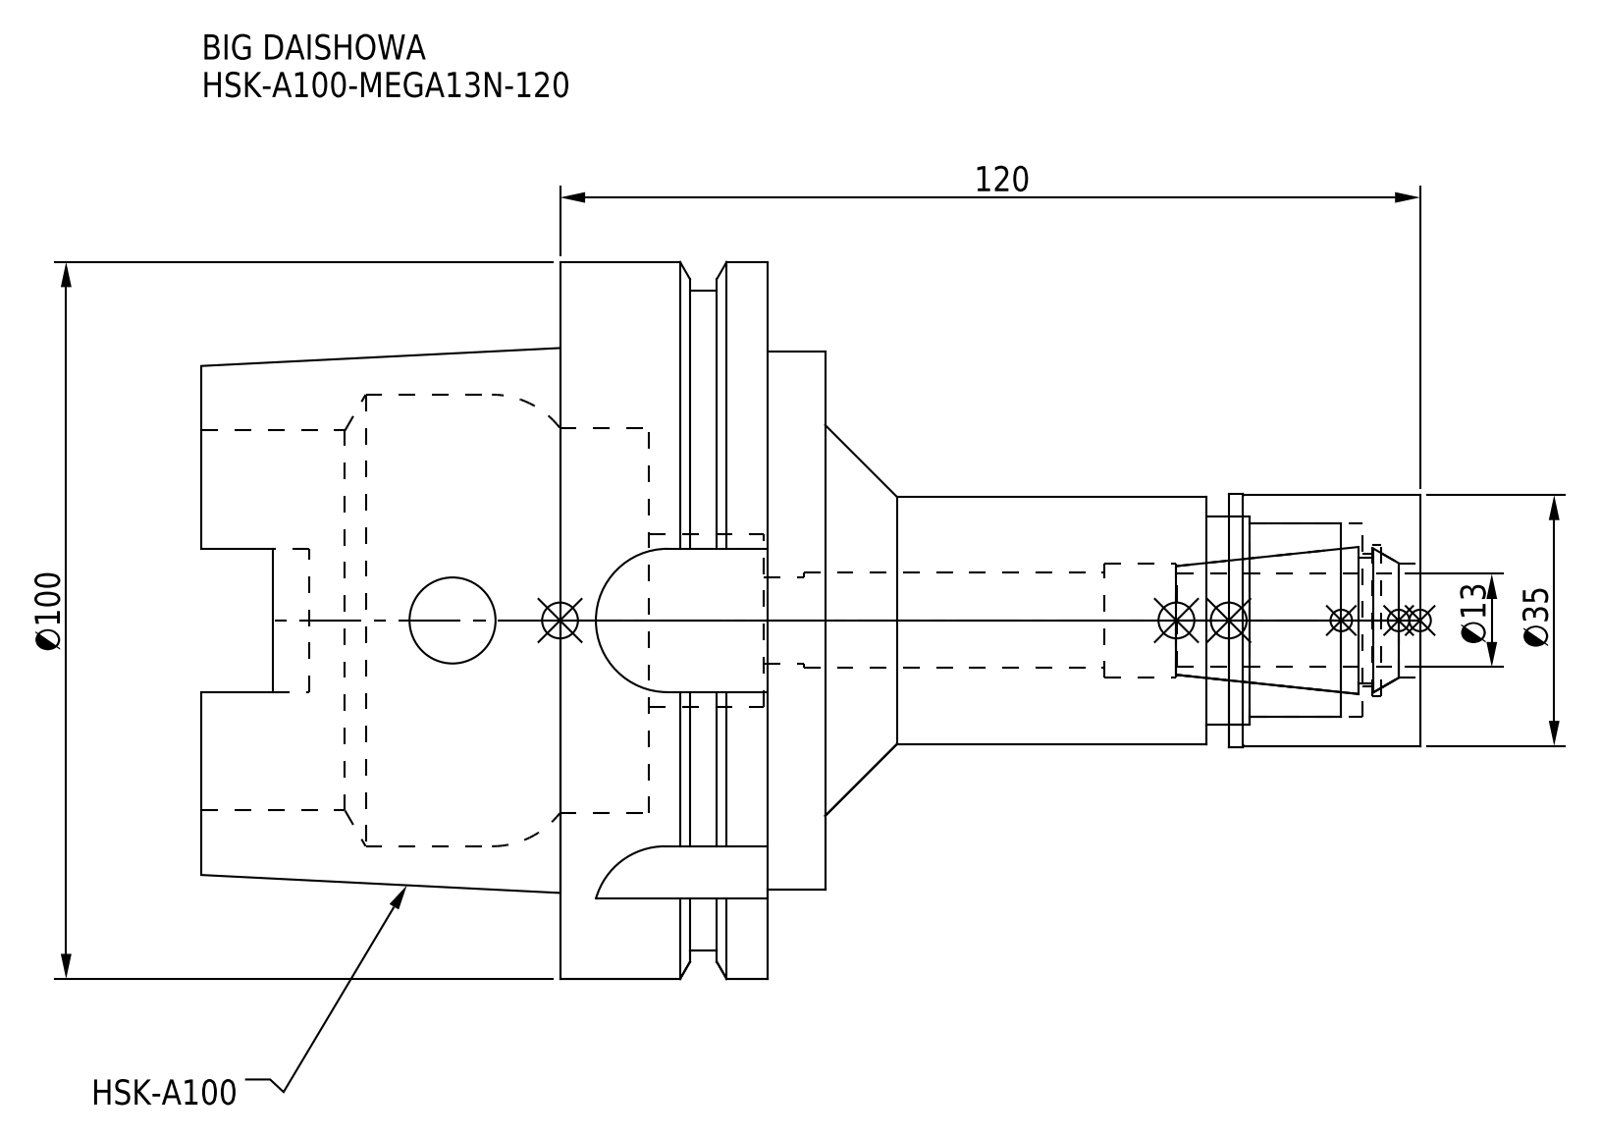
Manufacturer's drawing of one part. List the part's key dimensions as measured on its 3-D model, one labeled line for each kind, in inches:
Part name (STEP PRODUCT): HSK-A100-MEGA13N-120_1.stp; HSK-A100-MEGA13N-120-130-FreeParts; HSK-A100-MEGA13N-120; MGN13_1.stp (+3 more)
STEP written by: SolidWorks 2019 (CONFIG_CONTROL_DESIGN)
Units: inches
Bodies: 2 solids, 124 faces (44 planar, 58 cylindrical, 22 other)
Overall size (bounding box): 6.693 × 3.937 × 3.937
Volume: 21.67 in³ · Surface area: 106.7 in²
Round holes (diameter × count): ⌀0.472 ×2, ⌀0.524 ×1, ⌀0.63 ×1, ⌀0.728 ×1, ⌀0.827 ×1, ⌀0.945 ×1, ⌀1.063 ×1, ⌀1.142 ×1, ⌀2.087 ×1, ⌀2.118 ×1, ⌀2.48 ×1
Round bosses / shafts (diameter × count): ⌀3.937 ×1, ⌀3.622 ×1, ⌀2.953 ×1, ⌀1.39 ×1, ⌀1.378 ×1, ⌀1.358 ×1
Partial cylindrical surfaces — rounded edges, fillets, slot ends (radius × count): R0.192 ×4, R0.394 ×4
Main face-to-face distances: 1.142, 0.315, 1.457, 0.967, 0.652, 0.49, 3.268, 3.425, 3.11, 2.459
